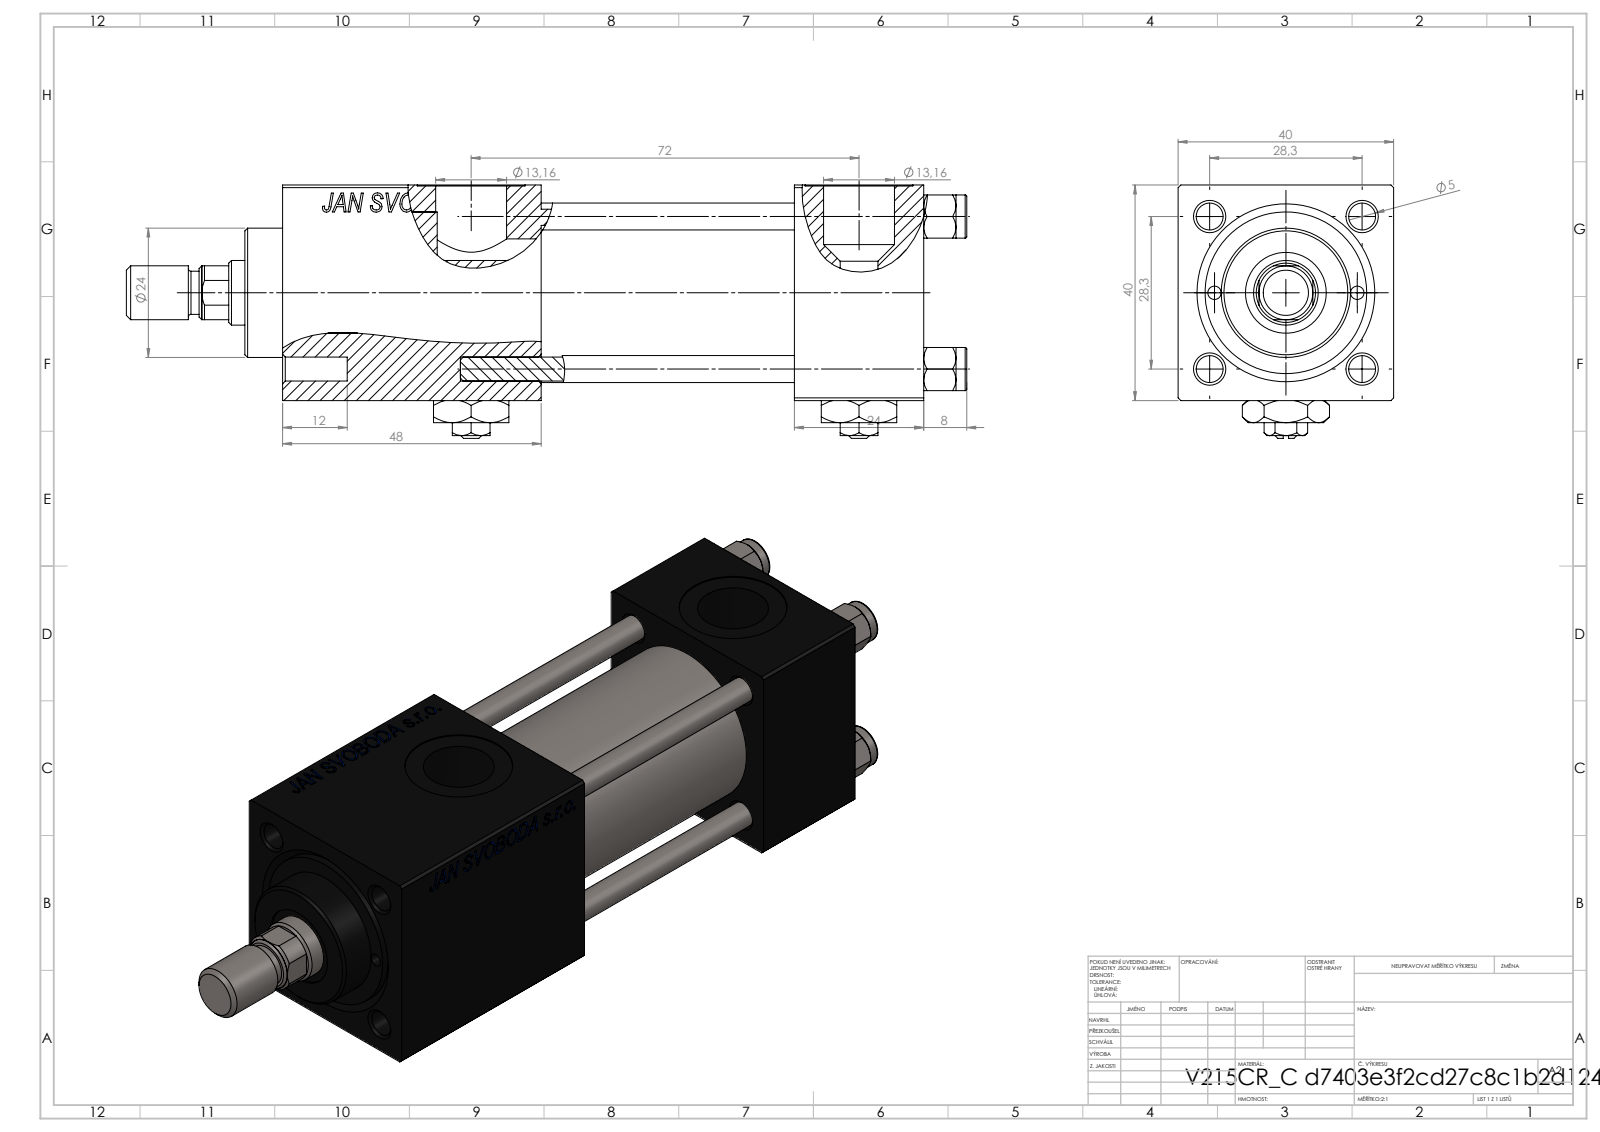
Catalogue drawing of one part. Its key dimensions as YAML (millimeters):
part_name: "NUT_M5_C; ROD_END_AH; V215CR_C_TYCINKA; Zatka_pro_OIL_PORT (+3 more)"
step_written_by: "SolidWorks 2019 (CONFIG_CONTROL_DESIGN)"
units: millimeters
bodies: {solids: 14, faces: 1268, planar: 578, cylindrical: 106, other: 584}
overall_size: [156, 47, 40]
volume: 141565
surface_area: 56963
round_holes:
  - {diameter: 5, count: 4}
  - {diameter: 20, count: 3}
  - {diameter: 2.5, count: 2}
  - {diameter: 7, count: 2}
  - {diameter: 13.16, count: 2}
  - {diameter: 6.5, count: 1}
  - {diameter: 12, count: 1}
  - {diameter: 15, count: 1}
  - {diameter: 25, count: 1}
  - {diameter: 30, count: 1}
round_bosses_or_shafts:
  - {diameter: 8, count: 5}
  - {diameter: 31, count: 1}
  - {diameter: 24, count: 1}
  - {diameter: 10, count: 1}
partial_cylinders:
  - {radius: 5.5, count: 1}
face_to_face_distances: [40, 24, 39.8, 48, 90.3, 66.3, 71, 47, 19.3, 95]
hole_center_spacings: [14.18, 20.01, 28.3, 30.84, 13.25, 40.02, 26.5, 72]
